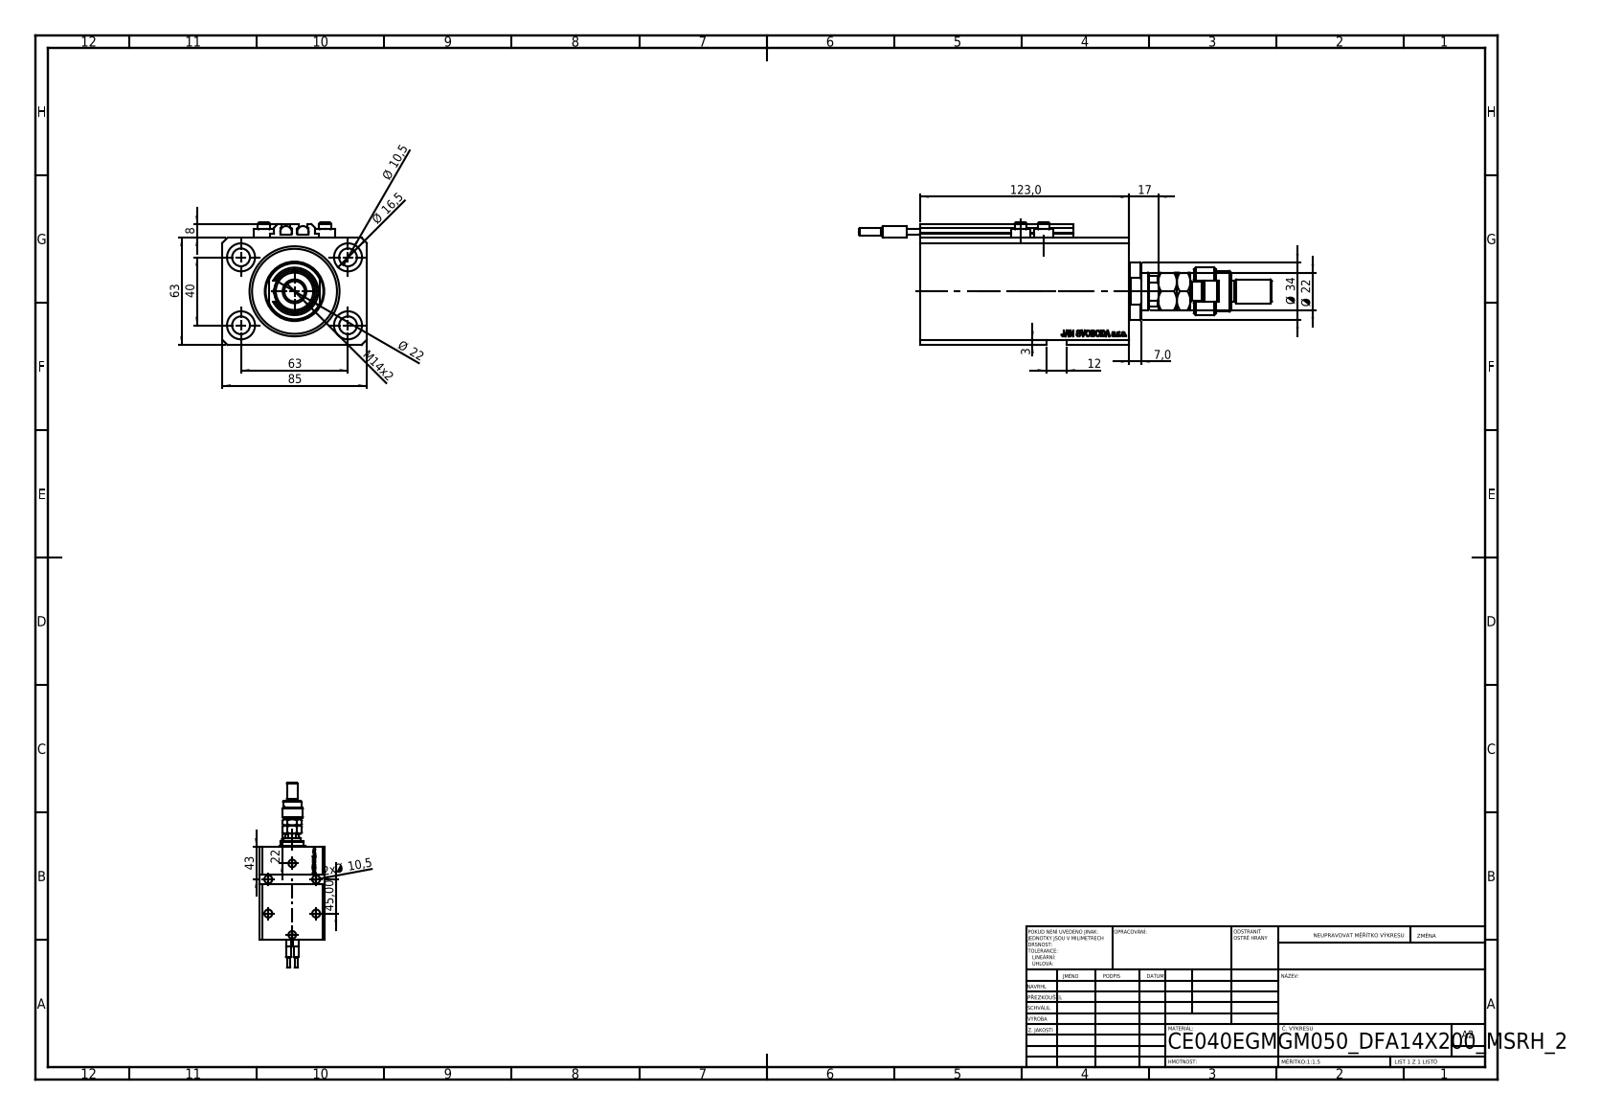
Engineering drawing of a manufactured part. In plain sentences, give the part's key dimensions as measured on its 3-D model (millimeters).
The part is named "MFA; V250CE_VC_E; V250CE_E_Body; FEMALE_PART_FOR_DFA (+3 more)". Its 3-D file was written by "SolidWorks 2019 (CONFIG_CONTROL_DESIGN)". It is 12 solids with 1244 faces: 595 planar, 171 cylindrical and 478 other. Overall it measures 243 by 85 by 72 millimeters. Its volume is 582 126 cubic millimeters and its surface area 130 039 square millimeters. Round holes: 8 of diameter 10.5, 4 of diameter 1.25, 4 of diameter 4, 4 of diameter 16.5, 2 of diameter 10, 2 of diameter 13.16, 2 of diameter 20, 1 of diameter 12.5, 1 of diameter 22, 1 of diameter 40, 1 of diameter 53. Round bosses or shafts: 4 of diameter 11.6, 4 of diameter 7, 2 of diameter 6.8, 2 of diameter 6.5, 2 of diameter 4, 1 of diameter 34, 1 of diameter 28, 1 of diameter 24. Partial cylindrical surfaces (rounded edges, fillets, slot ends): 10 of radius 0.2, 1 of radius 9.75, 1 of radius 10.5. The main face-to-face distances are 63, 85, 17, 123, 106, 3, 11.4, 94.6, 111.6, 65. The hole center spacings are 37.31, 63, 13.6, 15.4, 24.96, 27.54, 33.62, 36.
